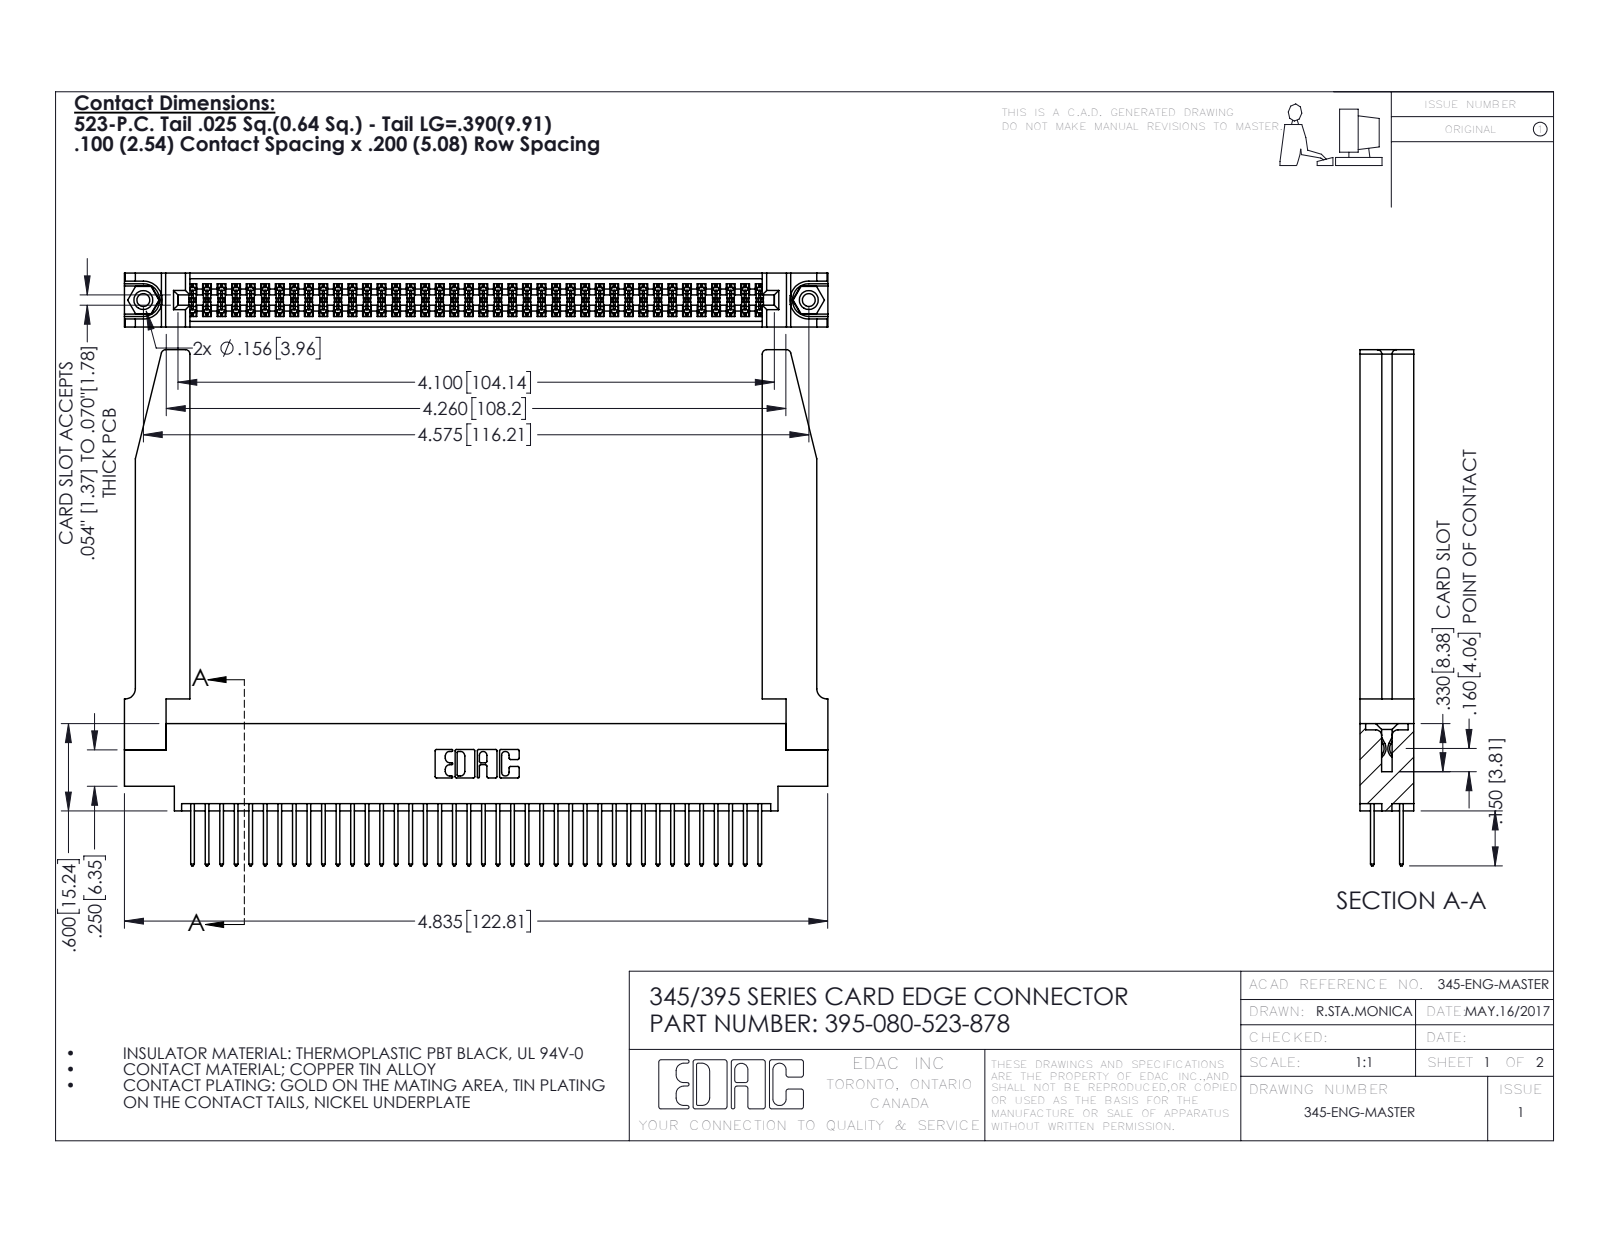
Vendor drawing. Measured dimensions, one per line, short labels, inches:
name: 345-292-001_345-293-123; 395-080-523-878; 345 Part_0.170 Offset - 0.156 Dia-TH; 345-250-001_345-250-001-102 (+1 more)
written by: SolidWorks 2016 (CONFIG_CONTROL_DESIGN)
unit: in
bodies: 85 solids, 4364 faces (2866 planar, 1446 cylindrical, 52 other)
size: 4.836 × 3.547 × 0.37
volume: 1.204 in³; area: 39.31 in²
holes: 2× ⌀0.089, 2× ⌀0.125, 2× ⌀0.156, 1× ⌀0.064
bosses: 2× ⌀0.155
rounds: 120× R0.006, 80× R0.01, 22× R0.01, 8× R0.03, 6× R0.007, 6× R0.031, 3× R0.026, 2× R0.014
face distances: 0.072, 0.37, 0.298, 0.098, 0.272, 0.025, 0.2, 0.225, 0.175, 0.148
hole spacings: 0.27, 4.339, 4.575
